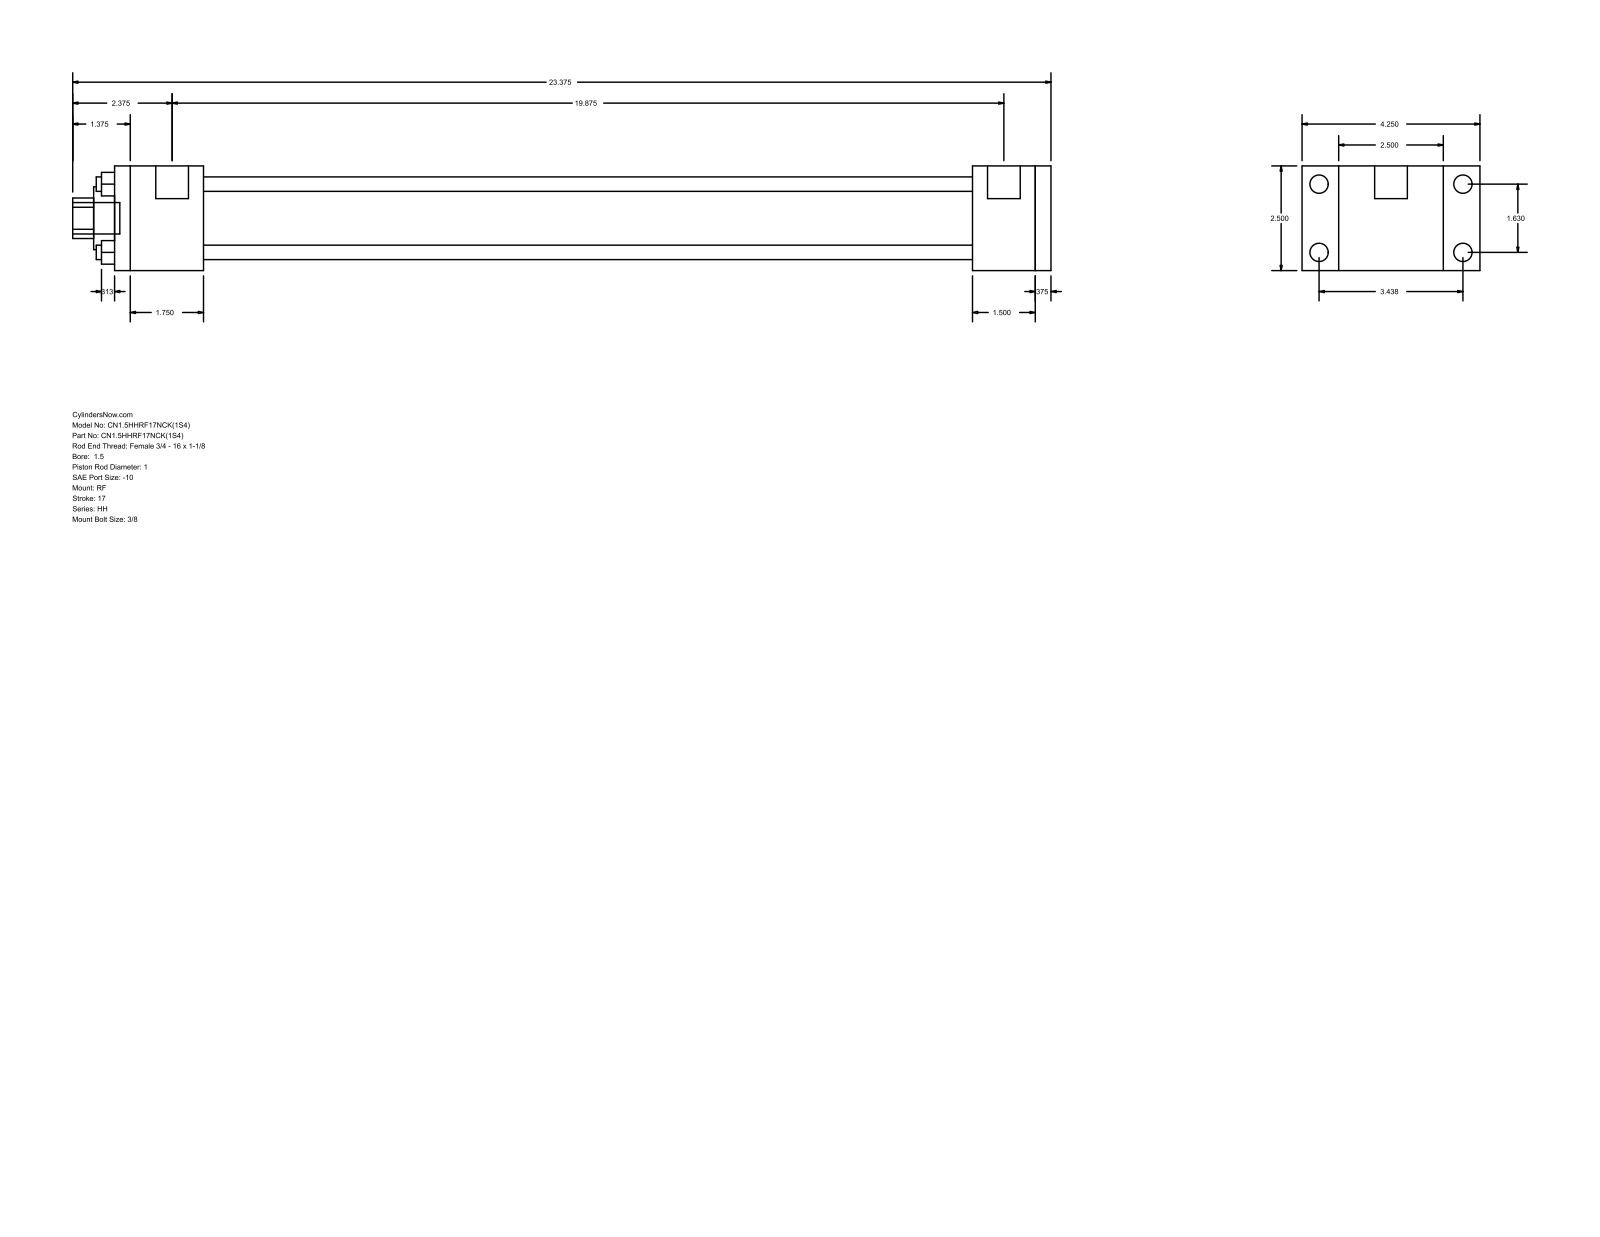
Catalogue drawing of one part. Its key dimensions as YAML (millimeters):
part_name: "HH_RF__0150_1"
step_written_by: "GSSL Pune (CONFIG_CONTROL_DESIGN)"
units: millimeters
bodies: {solids: 0, faces: 92, planar: 64, cylindrical: 28, other: 0}
overall_size: [593.73, 107.95, 63.5]
round_holes:
  - {diameter: 8.76, count: 4}
  - {diameter: 25.4, count: 1}
  - {diameter: 38.1, count: 1}
  - {diameter: 44.45, count: 1}
round_bosses_or_shafts:
  - {diameter: 11.13, count: 4}
  - {diameter: 5.56, count: 4}
  - {diameter: 19.84, count: 2}
  - {diameter: 19.05, count: 1}
partial_cylinders:
  - {radius: 12.29, count: 1}
face_to_face_distances: [63.5, 9.53, 466.72, 504.82, 514.35, 38.1, 47.63, 53.98, 520.7, 558.8]
hole_center_spacings: [29.27, 41.4, 58.55]
